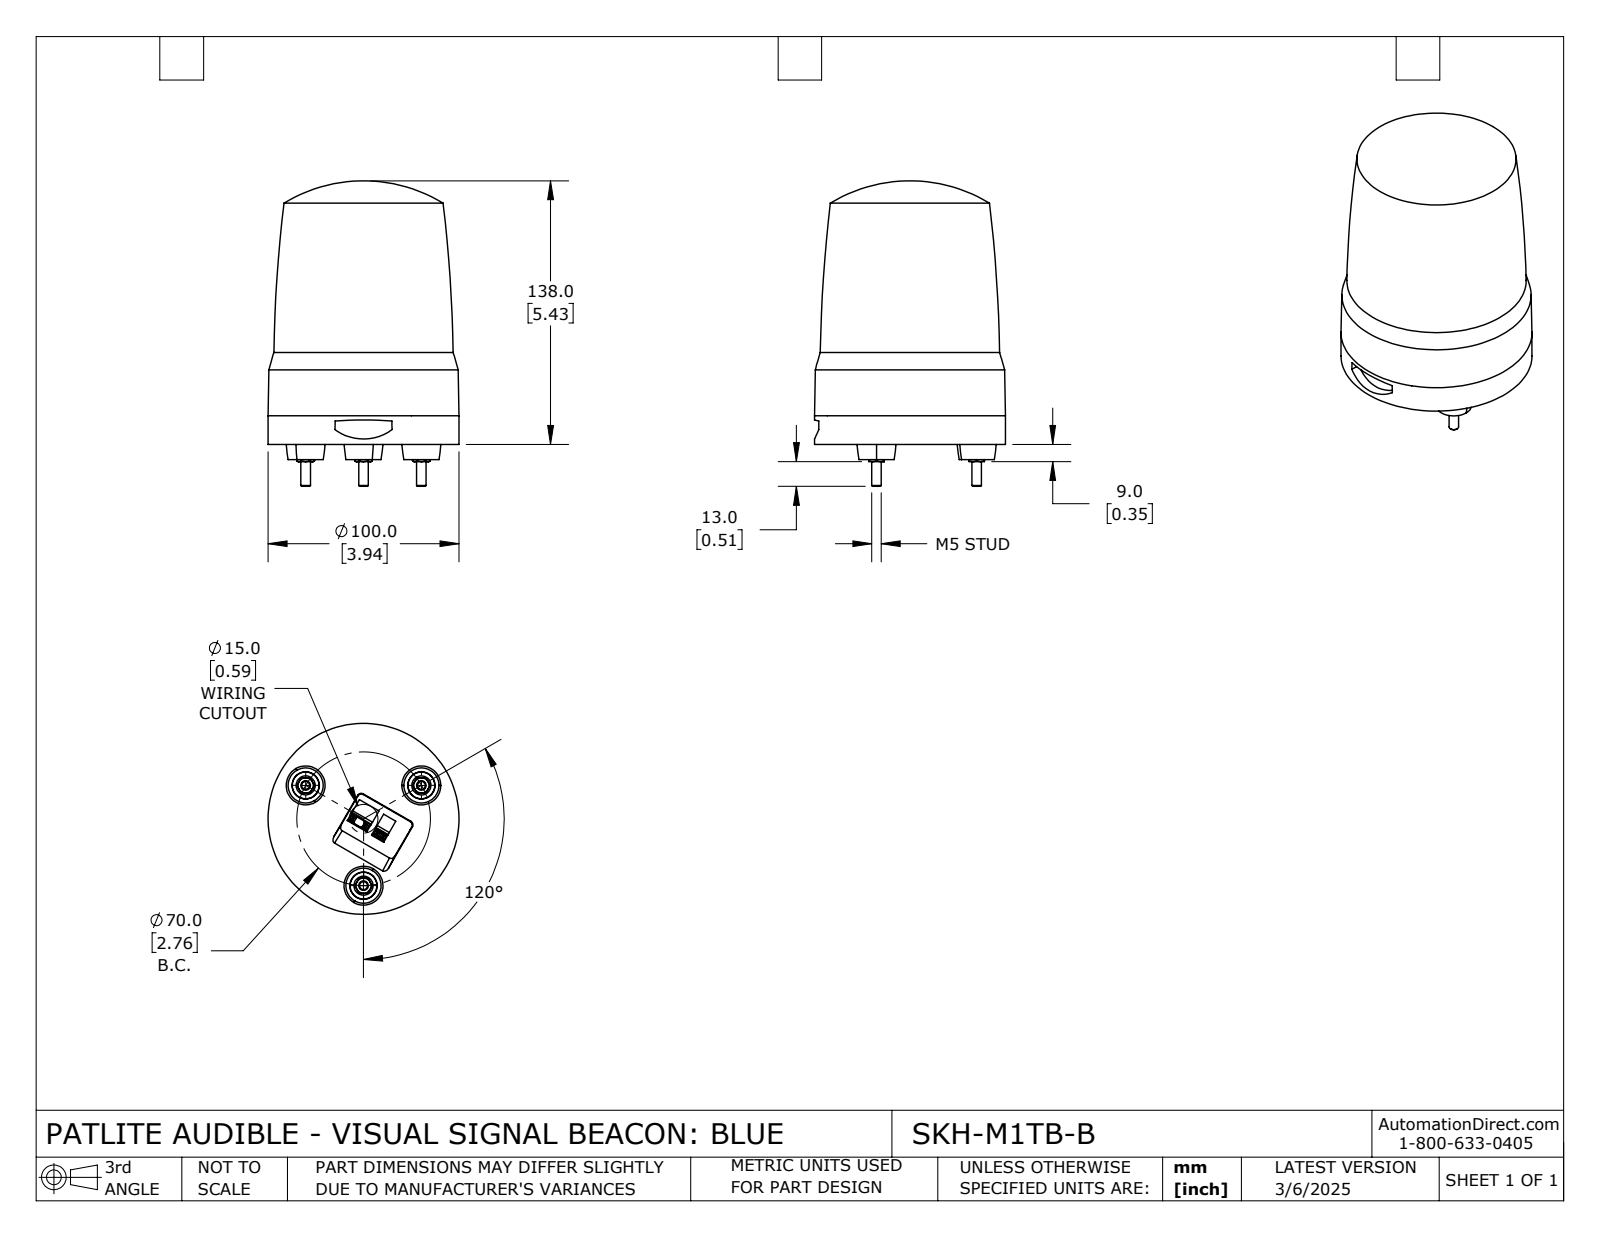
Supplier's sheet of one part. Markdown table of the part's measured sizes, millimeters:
| quantity | value |
| --- | --- |
| part name | SKH-M1TB-B |
| STEP written by | SolidWorks 2024 (CONFIG_CONTROL_DESIGN) |
| units | millimeters |
| bodies | 1 solid, 270 faces (146 planar, 25 cylindrical, 99 other) |
| overall size | 160 × 100 × 100 |
| volume | 895 705 mm³ |
| surface area | 57 629 mm² |
| round bosses / shafts (diameter × count) | 10 × 3, 5 × 3, 100 × 1 |
| partial cylindrical surfaces (radius × count) | 2 × 4, 0.3 × 2, 5.05 × 2, 45 × 1, 80.12 × 1 |
| main face-to-face distances | 18.85, 8, 22, 26.85, 3, 3.8, 4.2, 23.05, 5.95, 14.82 |
